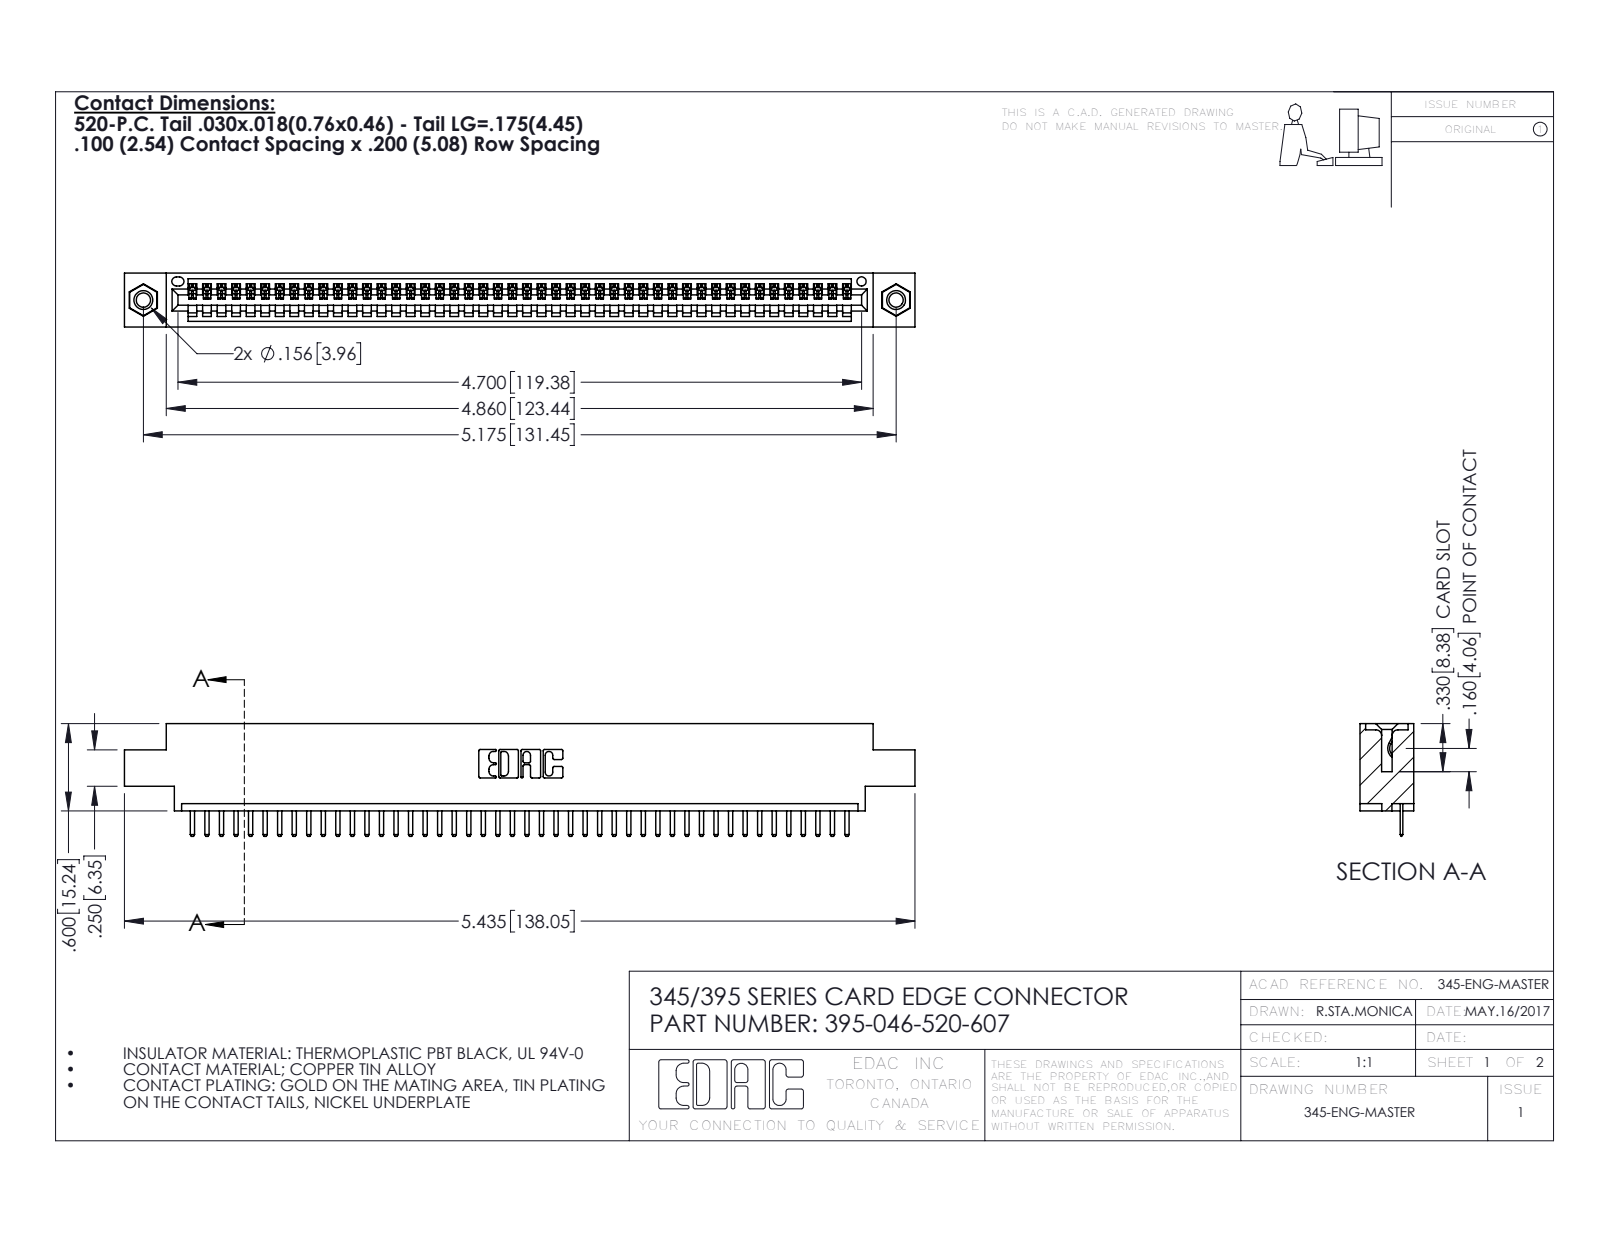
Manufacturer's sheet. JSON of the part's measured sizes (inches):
{"part_name": "395-046-520-607; 345-292-001_345-293-120; 345 Part_0.170 Offset - 0.156 Dia-TI; 345-250-001_345-250-005-103", "step_written_by": "SolidWorks 2016 (CONFIG_CONTROL_DESIGN)", "units": "inches", "bodies": {"solids": 49, "faces": 3042, "planar": 2048, "cylindrical": 978, "other": 16}, "overall_size": [5.435, 0.775, 0.37], "volume_in3": 0.786, "surface_area_in2": 26.2, "round_holes": [[0.098, 2], [0.125, 2], [0.156, 2], [0.064, 1]], "round_bosses_or_shafts": [[0.155, 2]], "partial_cylinders_radius": [[0.01, 94], [0.006, 92], [0.01, 22], [0.007, 6], [0.031, 6], [0.026, 3], [0.031, 2], [0.04, 2]], "face_to_face_distances": [0.072, 0.298, 0.37, 0.2, 0.098, 0.272, 0.025, 0.225, 0.072, 0.175], "hole_center_spacings": [0.27, 4.939, 5.175]}
